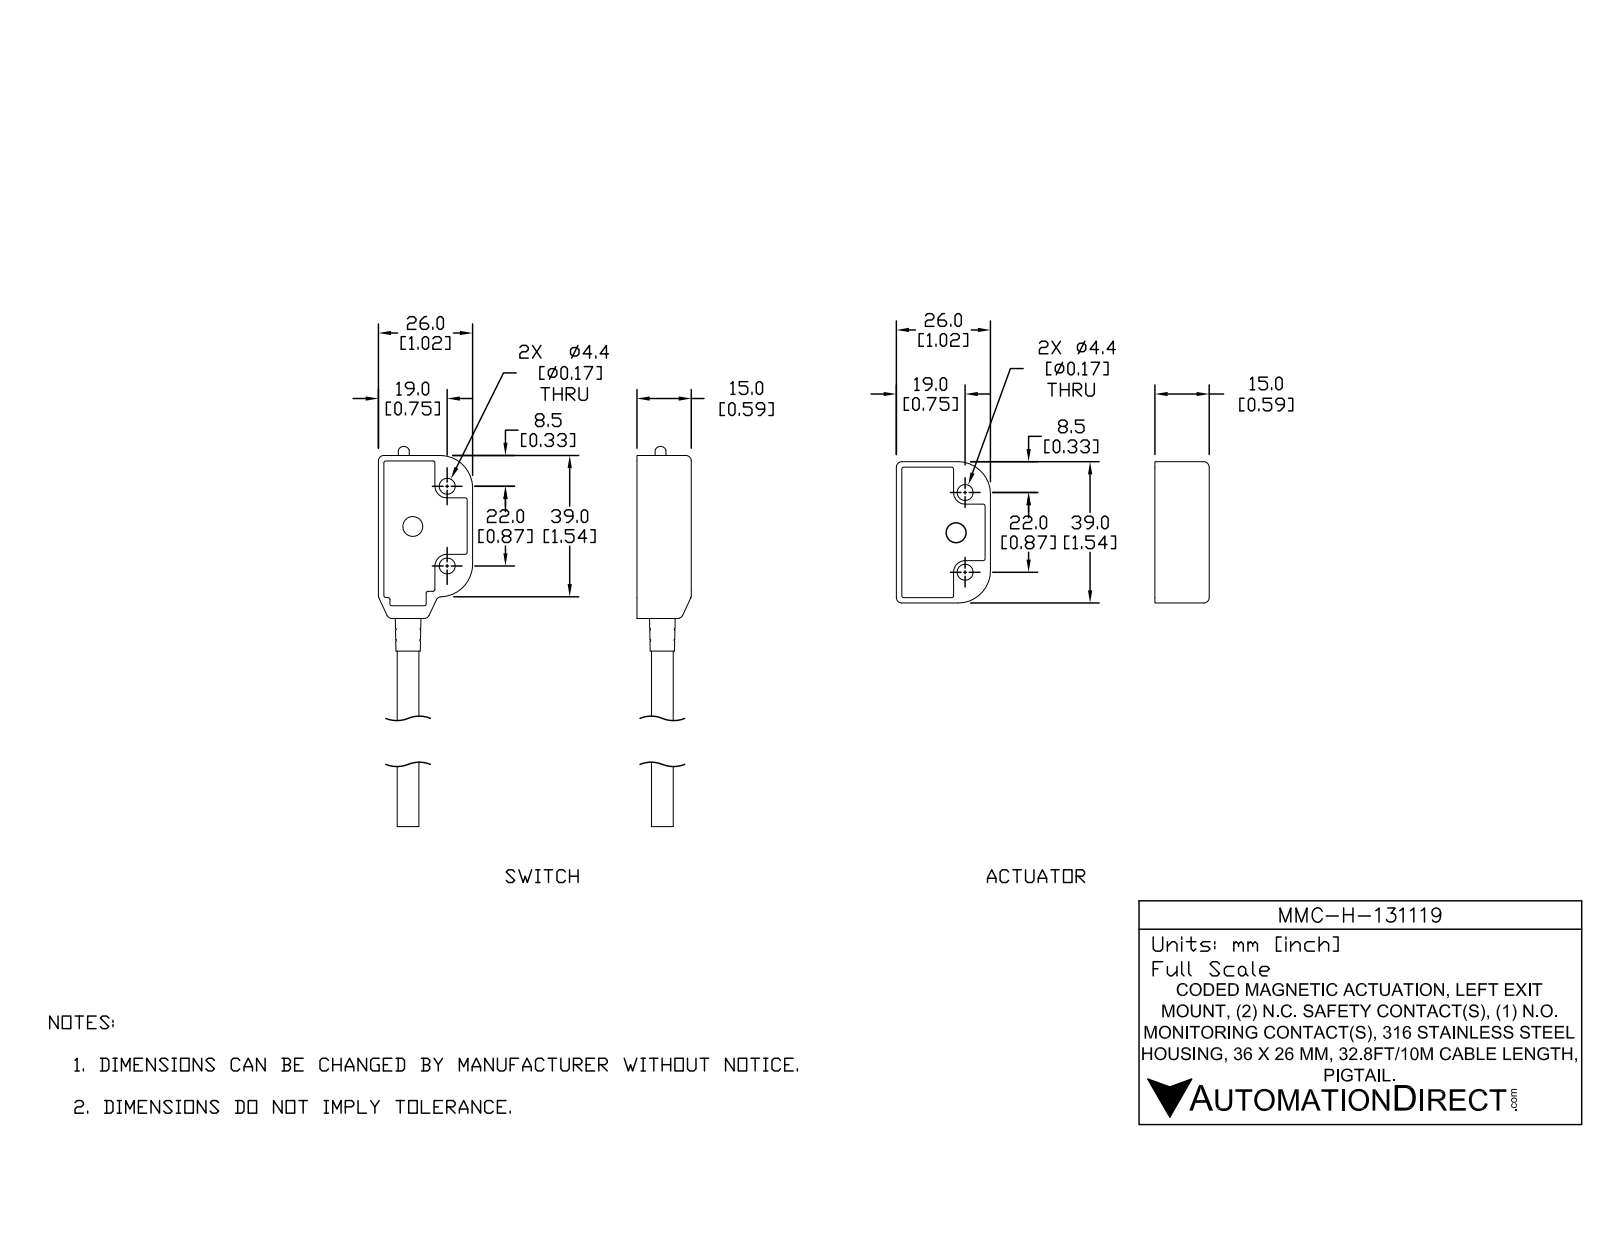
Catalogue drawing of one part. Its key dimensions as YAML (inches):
part_name: "MMC-H-131119; MMC-H-131119_2; MMC-H-131119_1"
step_written_by: "SolidWorks 2017 (AUTOMOTIVE_DESIGN)"
units: inches
bodies: {solids: 9, faces: 603, planar: 178, cylindrical: 234, other: 191}
overall_size: [7.902, 2.087, 0.591]
volume: 1.233
surface_area: 31
round_holes:
  - {diameter: 0.173, count: 4}
  - {diameter: 0.197, count: 2}
  - {diameter: 0.118, count: 1}
  - {diameter: 0.232, count: 1}
  - {diameter: 0.283, count: 1}
round_bosses_or_shafts:
  - {diameter: 0.079, count: 2}
  - {diameter: 0.031, count: 2}
  - {diameter: 0.339, count: 1}
  - {diameter: 0.299, count: 1}
  - {diameter: 0.28, count: 1}
  - {diameter: 0.236, count: 1}
  - {diameter: 0.157, count: 1}
partial_cylinders:
  - {radius: 0.02, count: 83}
  - {radius: 0.012, count: 26}
  - {radius: 0.059, count: 15}
  - {radius: 0.008, count: 8}
  - {radius: 0.157, count: 6}
  - {radius: 0.126, count: 4}
  - {radius: 0.13, count: 4}
  - {radius: 0.181, count: 4}
face_to_face_distances: [0.059, 0.575, 0.516, 0.098, 0.461, 0.52, 0.055, 0.591, 0.531, 0.965]
hole_center_spacings: [0.572, 0.866, 1.239, 1.535, 1.763, 0.076, 0.44, 0.448]
